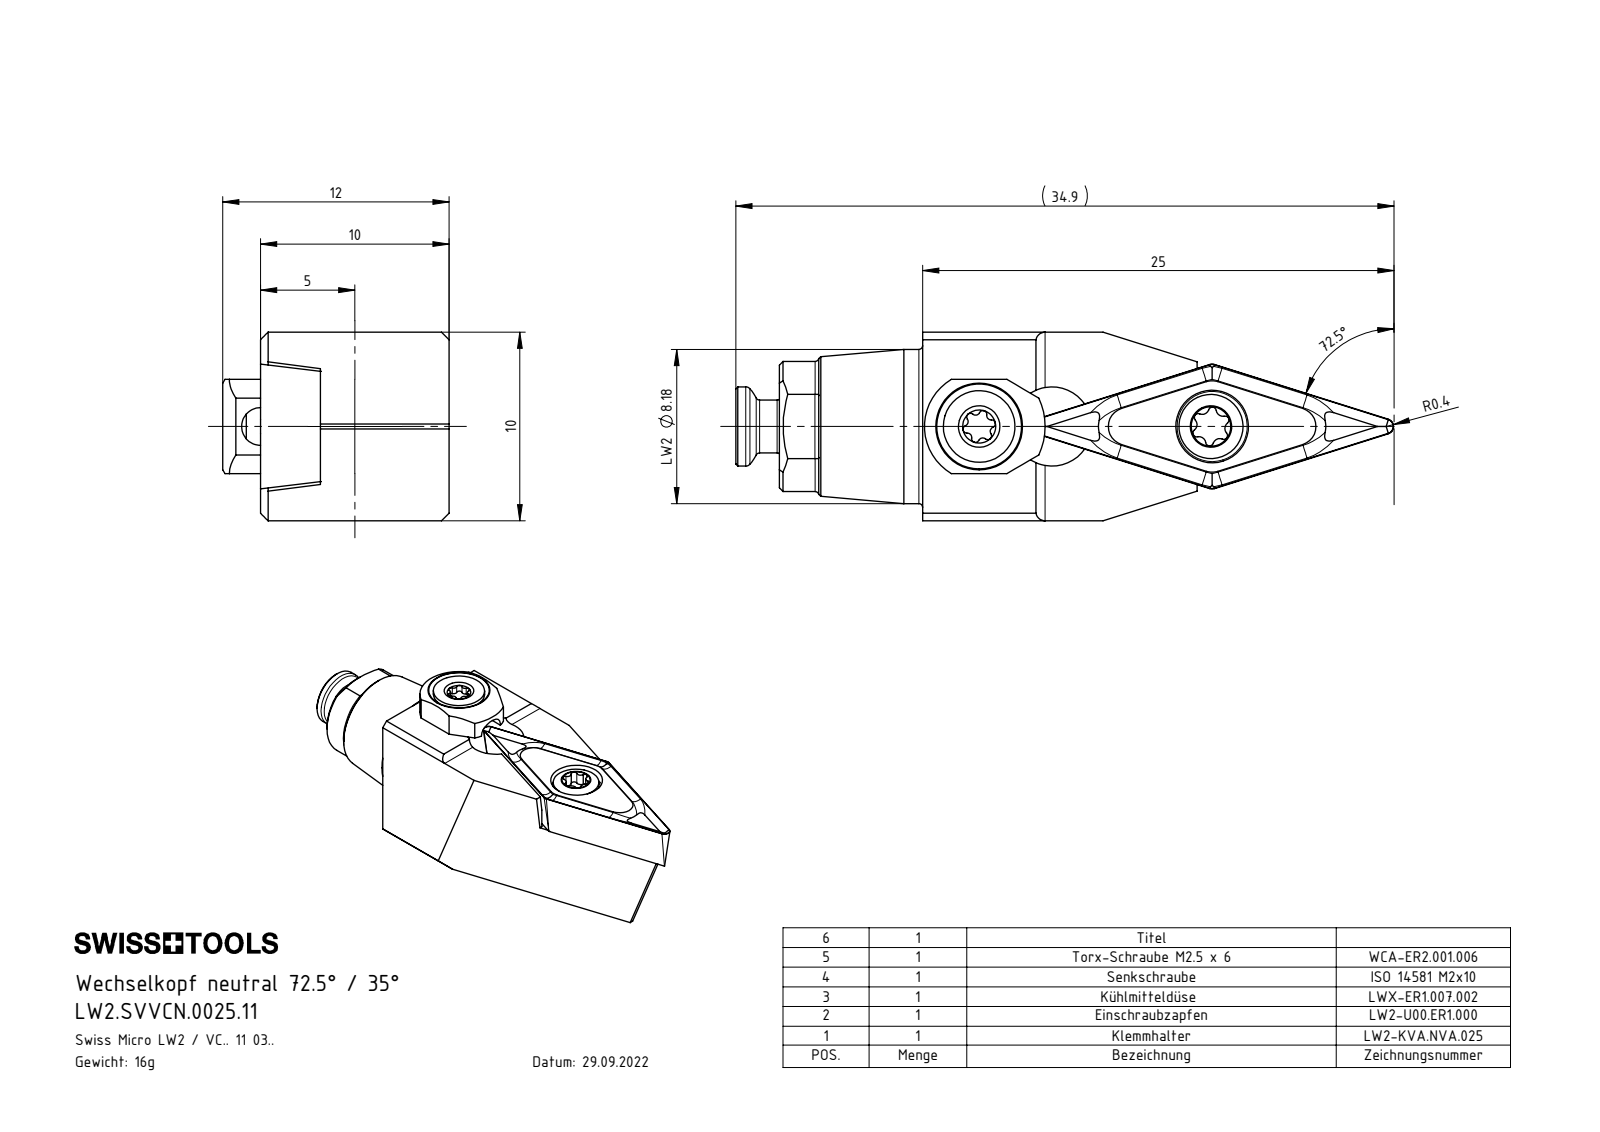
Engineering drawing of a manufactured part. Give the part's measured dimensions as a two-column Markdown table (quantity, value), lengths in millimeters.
| quantity | value |
| --- | --- |
| part name | ISO 14581 - M2x10; LW2.SVVCN.0025.11; LW2-KVA.NVA.025_A; LW2-U00.ER1.000_A (+3 more) |
| STEP written by | SolidWorks 2022 (CONFIG_CONTROL_DESIGN) |
| units | millimeters |
| bodies | 6 solids, 264 faces (65 planar, 98 cylindrical, 101 other) |
| overall size | 34.88 × 13.5 × 10 |
| volume | 1 886 mm³ |
| surface area | 1 957 mm² |
| round holes (diameter × count) | 1 × 1, 1.5 × 1, 1.6 × 1, 2 × 1, 2.05 × 1, 2.8 × 1, 3 × 1, 3.5 × 1, 3.85 × 1, 4.2 × 1 |
| round bosses / shafts (diameter × count) | 8.18 × 1, 4.2 × 1, 4 × 1, 3.8 × 1, 3.4 × 1, 3 × 1, 2.8 × 1, 2.5 × 1 |
| partial cylindrical surfaces (radius × count) | 0.2 × 8, 0.19 × 6, 0.21 × 6, 0.24 × 6, 0.29 × 6, 0.36 × 5, 0.36 × 1, 0.5 × 1 |
| main face-to-face distances | 10, 6.82, 3.18, 0.4, 9.6, 2.78, 7.6, 2.5, 7.5, 2 |
| hole center spacings | 3.86, 8.43, 8.5, 12.29, 12.36 |
